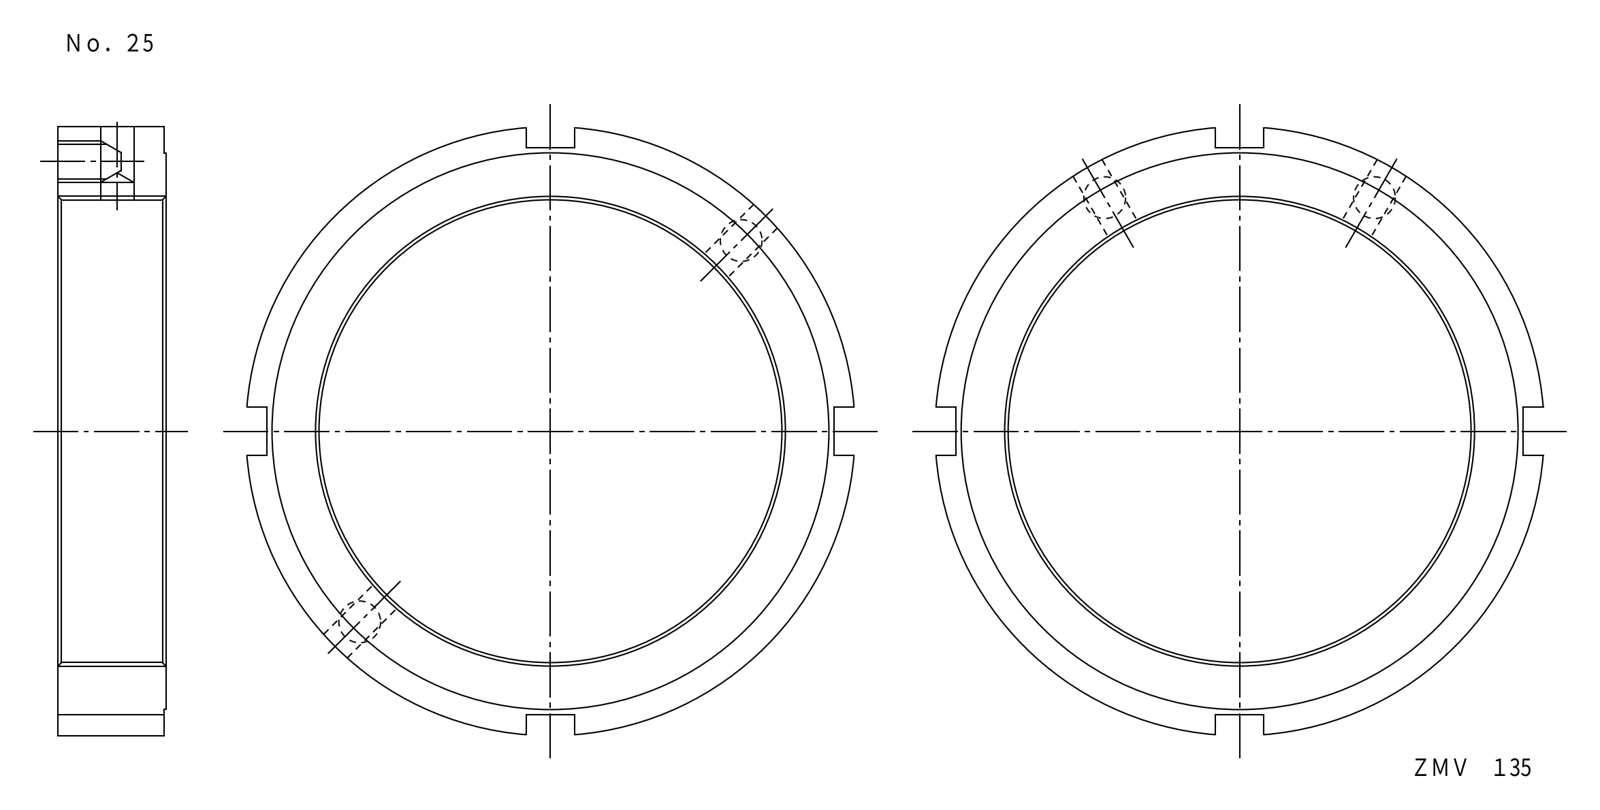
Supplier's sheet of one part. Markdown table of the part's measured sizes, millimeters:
| quantity | value |
| --- | --- |
| part name | FKD ZMV135 |
| STEP written by | Autodesk Inventor LT (CONFIG_CONTROL_DESIGN) |
| units | millimeters |
| bodies | 1 solid, 29 faces (15 planar, 10 cylindrical, 4 other) |
| overall size | 174.44 × 174.44 × 31 |
| volume | 284 857 mm³ |
| surface area | 51 828 mm² |
| round holes (diameter × count) | 9.6 × 2, 10.11 × 2, 135 × 1 |
| round bosses / shafts (diameter × count) | 175 × 1, 160 × 1 |
| main face-to-face distances | 31, 0.5, 30.5, 74.5, 88.5, 163, 14 |
| hole center spacings | 77.5, 155 |
